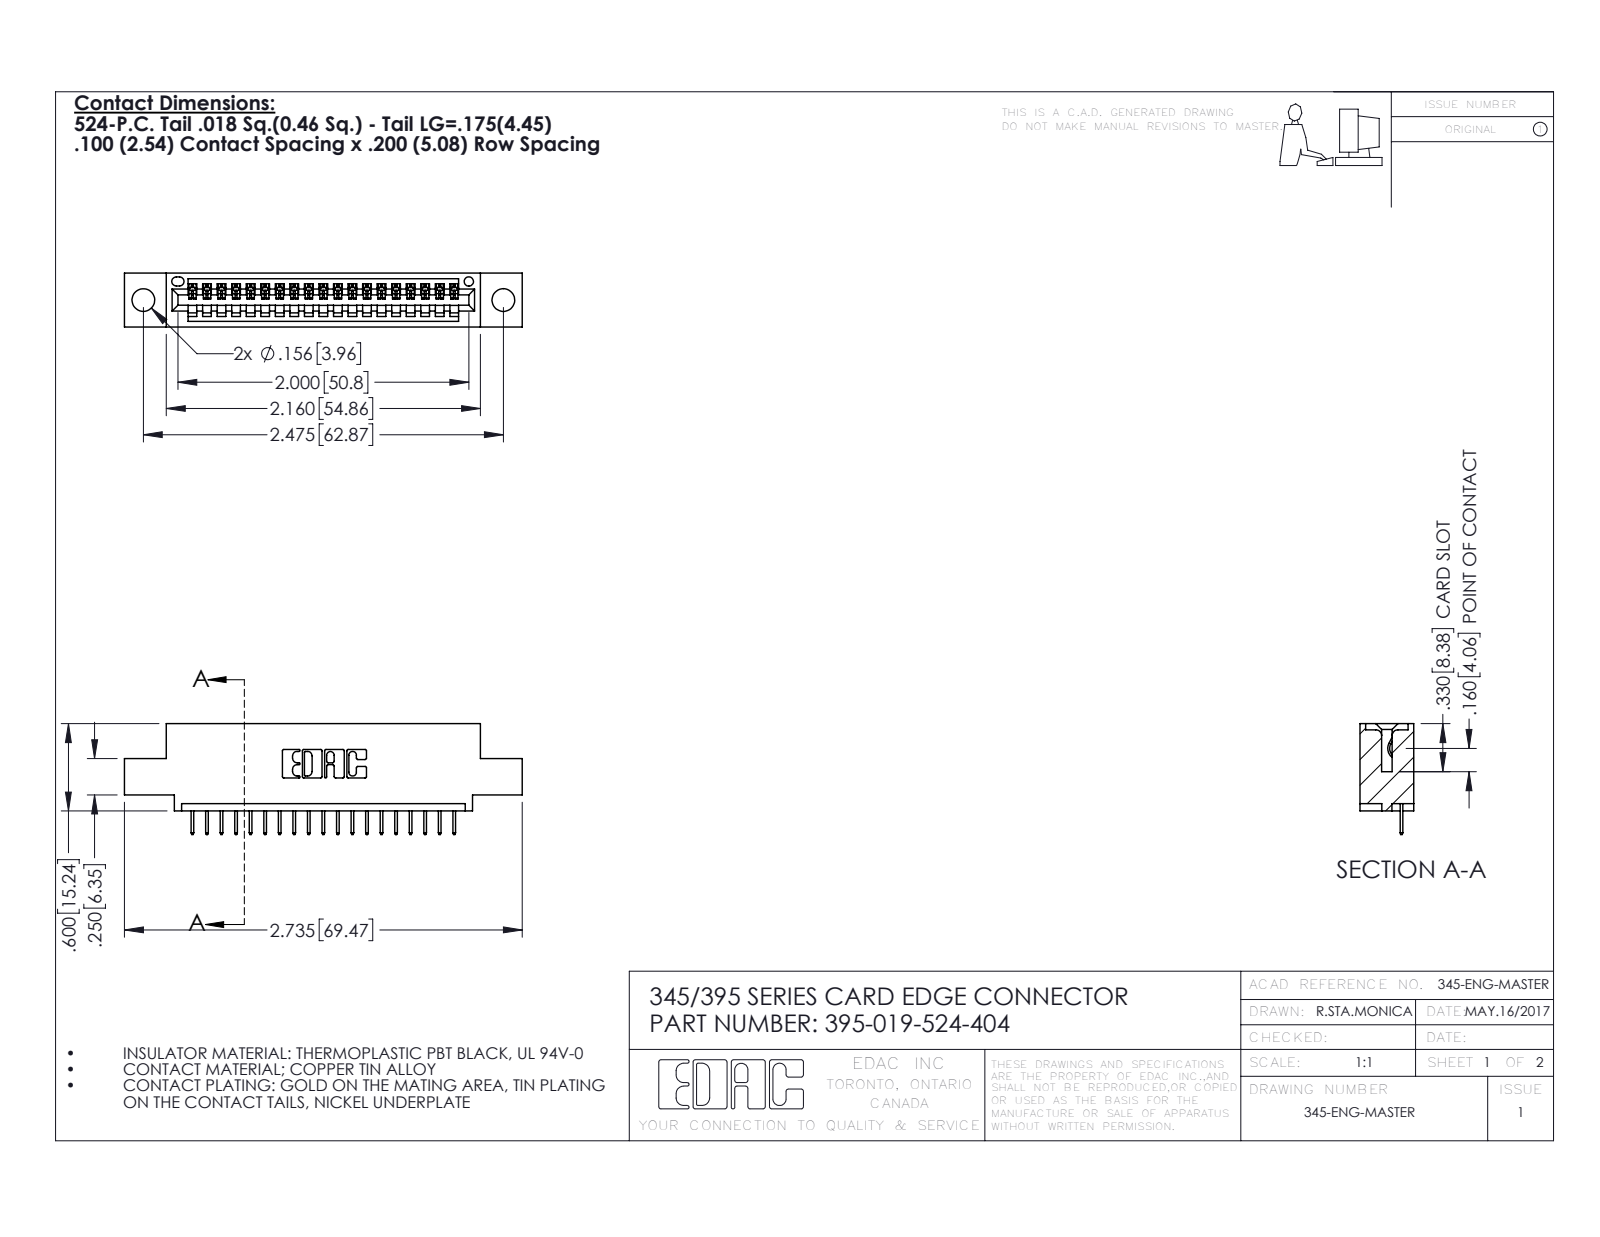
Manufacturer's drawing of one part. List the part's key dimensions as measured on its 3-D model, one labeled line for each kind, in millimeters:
Part name (STEP PRODUCT): 395-019-524-404; 345-292-001_345-293-124; 345 Part_0.110 Offset - 0.156 Dia-TH
STEP written by: SolidWorks 2016 (CONFIG_CONTROL_DESIGN)
Units: millimetres
Bodies: 20 solids, 1308 faces (958 planar, 350 cylindrical, 0 other)
Overall size (bounding box): 69.5 × 19.4 × 9.4
Volume: 6 180 mm³ · Surface area: 7 542 mm²
Round holes (diameter × count): ⌀4 ×2, ⌀1.6 ×1
Partial cylindrical surfaces — rounded edges, fillets, slot ends (radius × count): R0.2 ×38, R0.3 ×22, R0.2 ×6, R0.8 ×6, R0.7 ×3, R0.8 ×2, R1 ×2, R0.4 ×1
Main face-to-face distances: 1.8, 7.6, 9.4, 5.1, 2.5, 6.9, 0.6, 5.7, 1.8, 3.8
Hole centre spacings: 6.9, 56.9, 62.9
